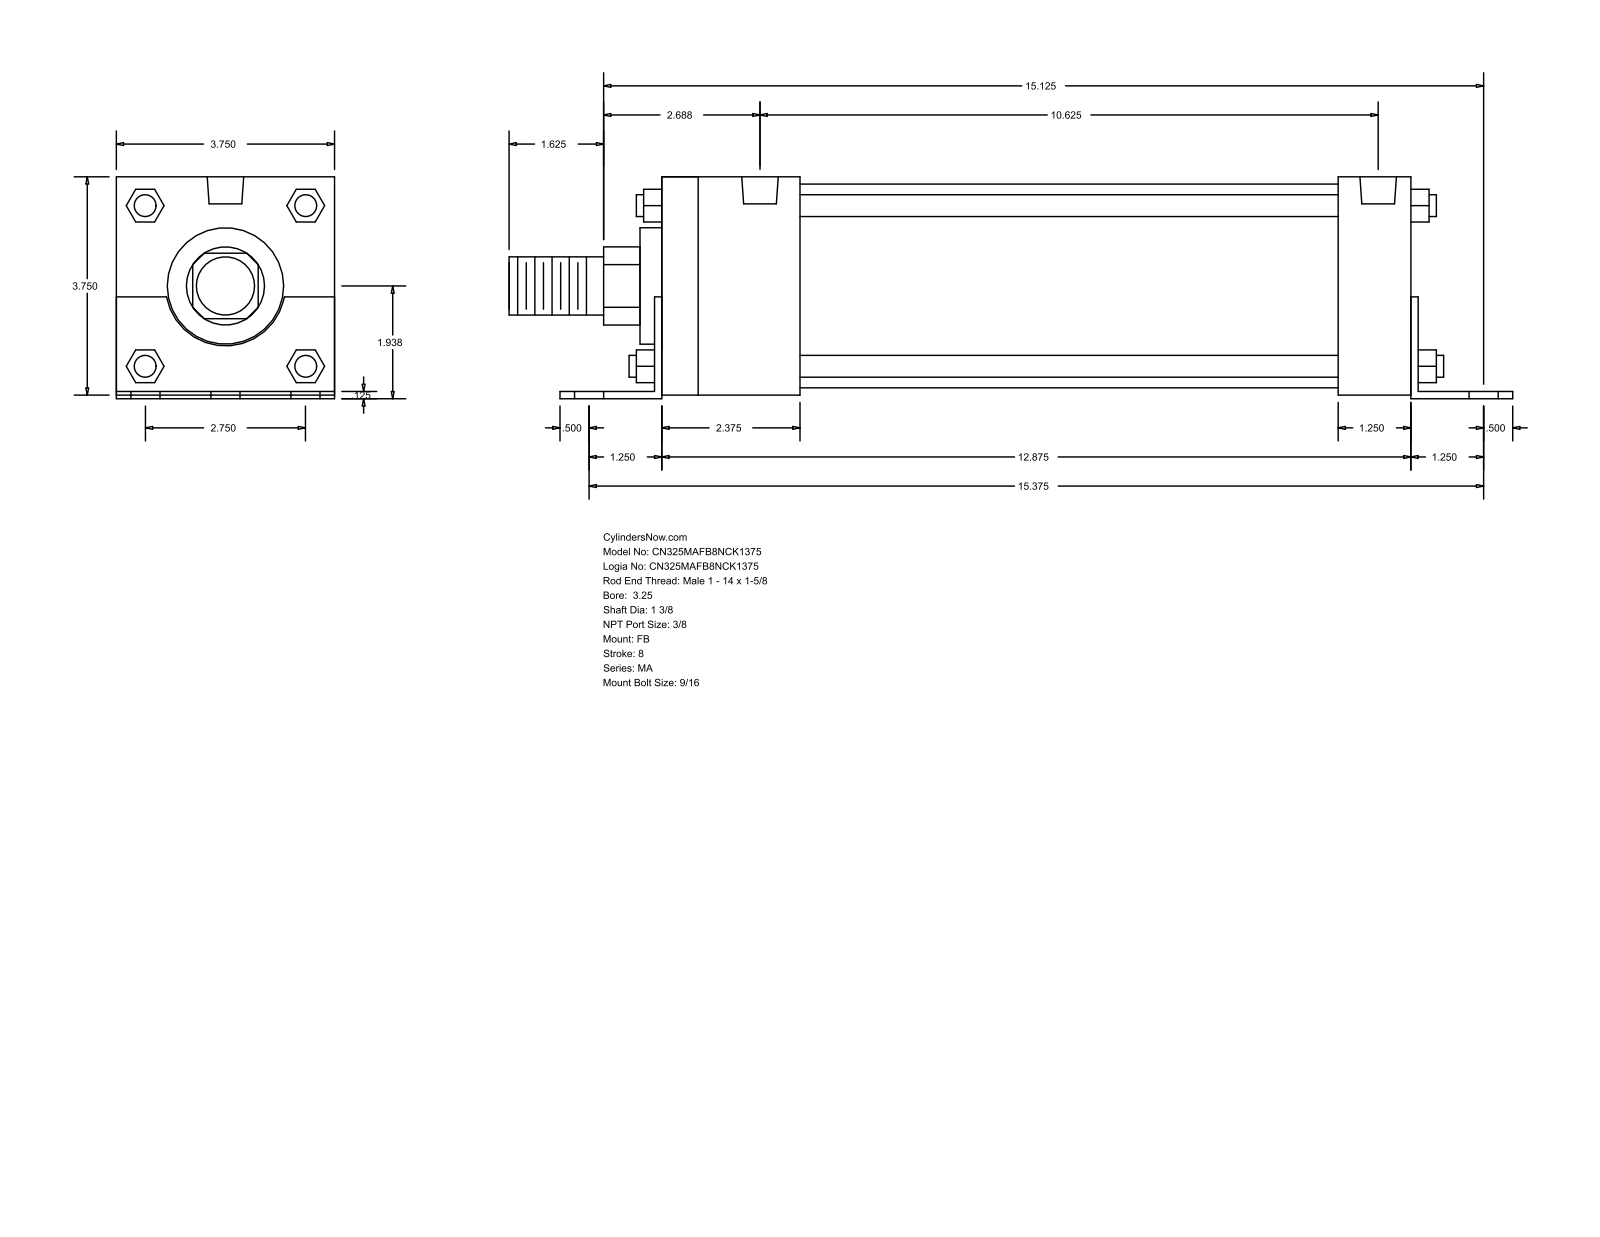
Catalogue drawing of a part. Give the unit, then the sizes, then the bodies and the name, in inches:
Units: inches
Overall size (bounding box): 17.25 × 3.813 × 3.75
Round holes (diameter × count): ⌀0.563 ×6, ⌀0.437 ×4, ⌀0.627 ×2
Round bosses / shafts (diameter × count): ⌀0.375 ×4, ⌀3.5 ×1, ⌀2 ×1, ⌀1.375 ×1, ⌀1 ×1
Partial cylindrical surfaces — rounded edges, fillets, slot ends (radius × count): R0.672 ×1, R1.03 ×1
Main face-to-face distances: 3.75, 0.125, 0.063, 3.812, 0.062, 3.687, 13, 12.875, 1.25, 1.375
Hole centre spacings: 1.375, 15.437, 15.375, 2.275, 2.427, 2.75, 3.243, 3.414
Bodies: 0 solids, 140 faces (105 planar, 35 cylindrical, 0 other)
Part name (STEP PRODUCT): MA_FB__0325_1.375
STEP written by: GSSL Pune (CONFIG_CONTROL_DESIGN)
